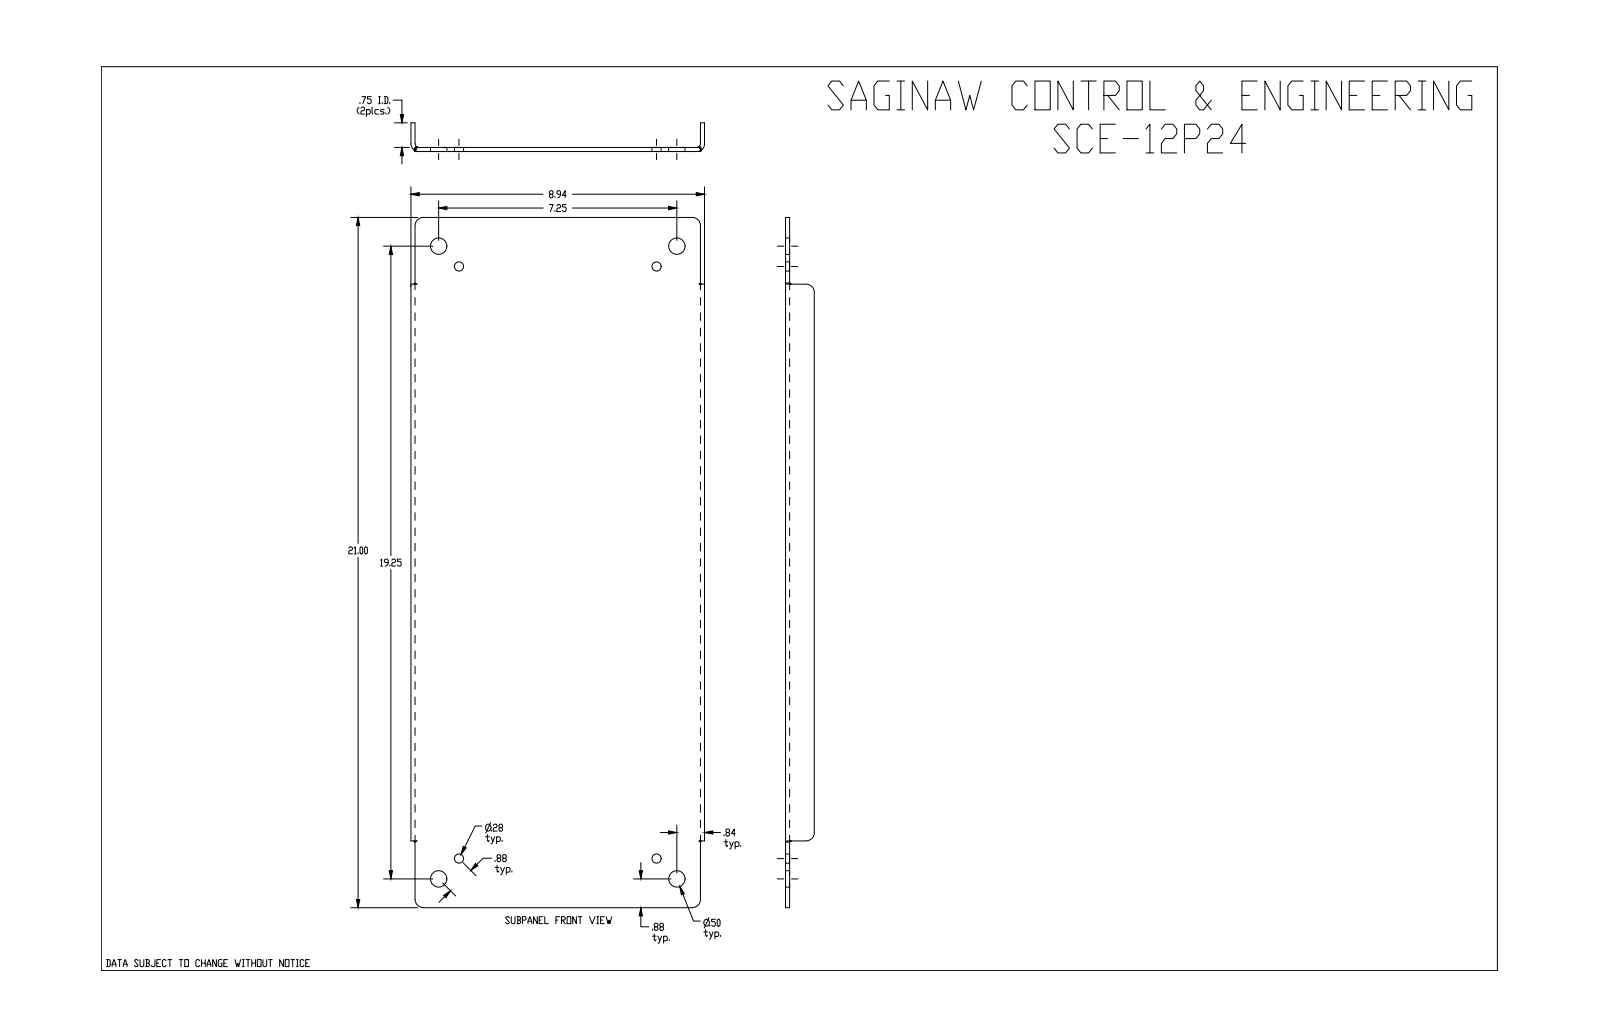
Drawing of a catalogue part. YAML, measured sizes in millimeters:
part_name: "SCE-12P24"
step_written_by: "SolidWorks 2019 (CONFIG_CONTROL_DESIGN)"
units: millimeters
bodies: {solids: 1, faces: 50, planar: 18, cylindrical: 20, other: 12}
overall_size: [533.4, 227, 22.2]
volume: 426900
surface_area: 274600
round_holes:
  - {diameter: 7.1, count: 4}
  - {diameter: 12.7, count: 4}
partial_cylinders:
  - {radius: 6.4, count: 6}
  - {radius: 2.8, count: 2}
  - {radius: 6, count: 2}
face_to_face_distances: [3.2, 3.2, 223.9, 220.6, 227, 19.1, 22.2, 533.4, 51.6, 481.8]
hole_center_spacings: [22.2, 169.2, 473.5, 502.3, 152.7, 184.2, 457.5, 482.3]
